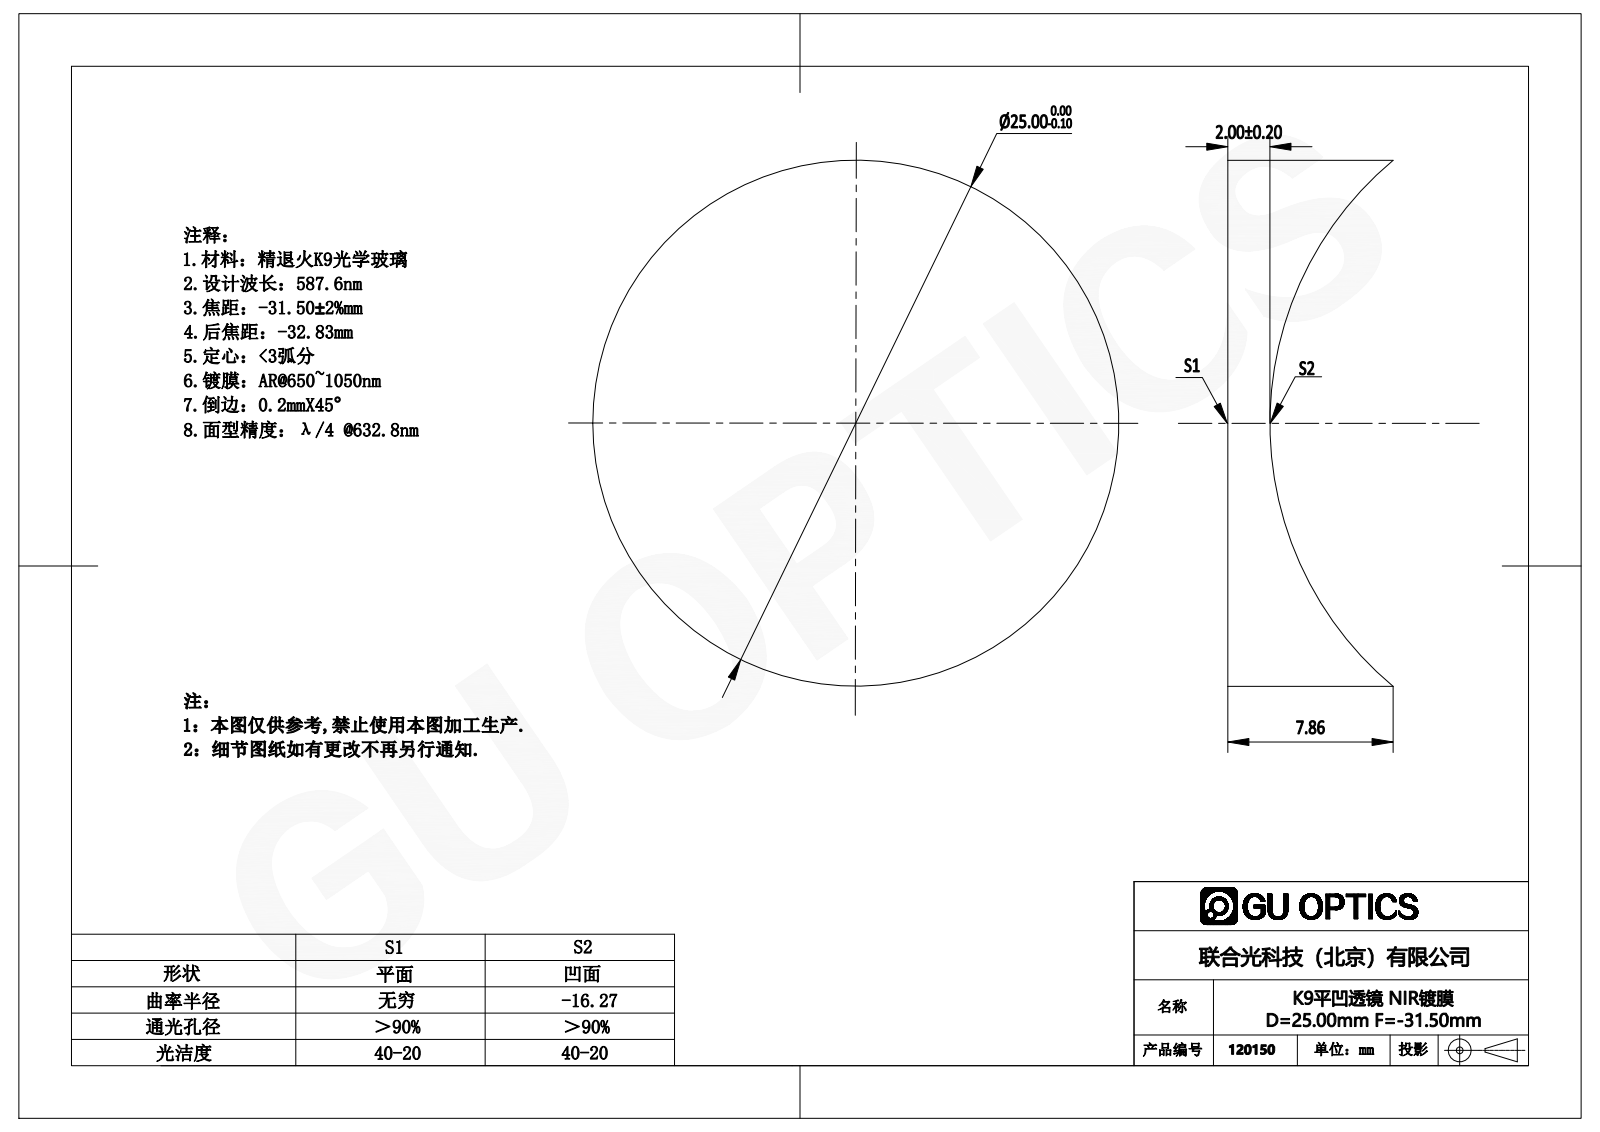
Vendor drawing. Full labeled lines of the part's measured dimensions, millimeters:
Part name (STEP PRODUCT): 120150
STEP written by: SolidWorks 2016 (AUTOMOTIVE_DESIGN)
Units: millimetres
Bodies: 1 solid, 5 faces (1 planar, 2 cylindrical, 2 other)
Overall size (bounding box): 25 × 25 × 7.86
Volume: 2 314 mm³ · Surface area: 1 706 mm²
Round bosses / shafts (diameter × count): ⌀25 ×1
